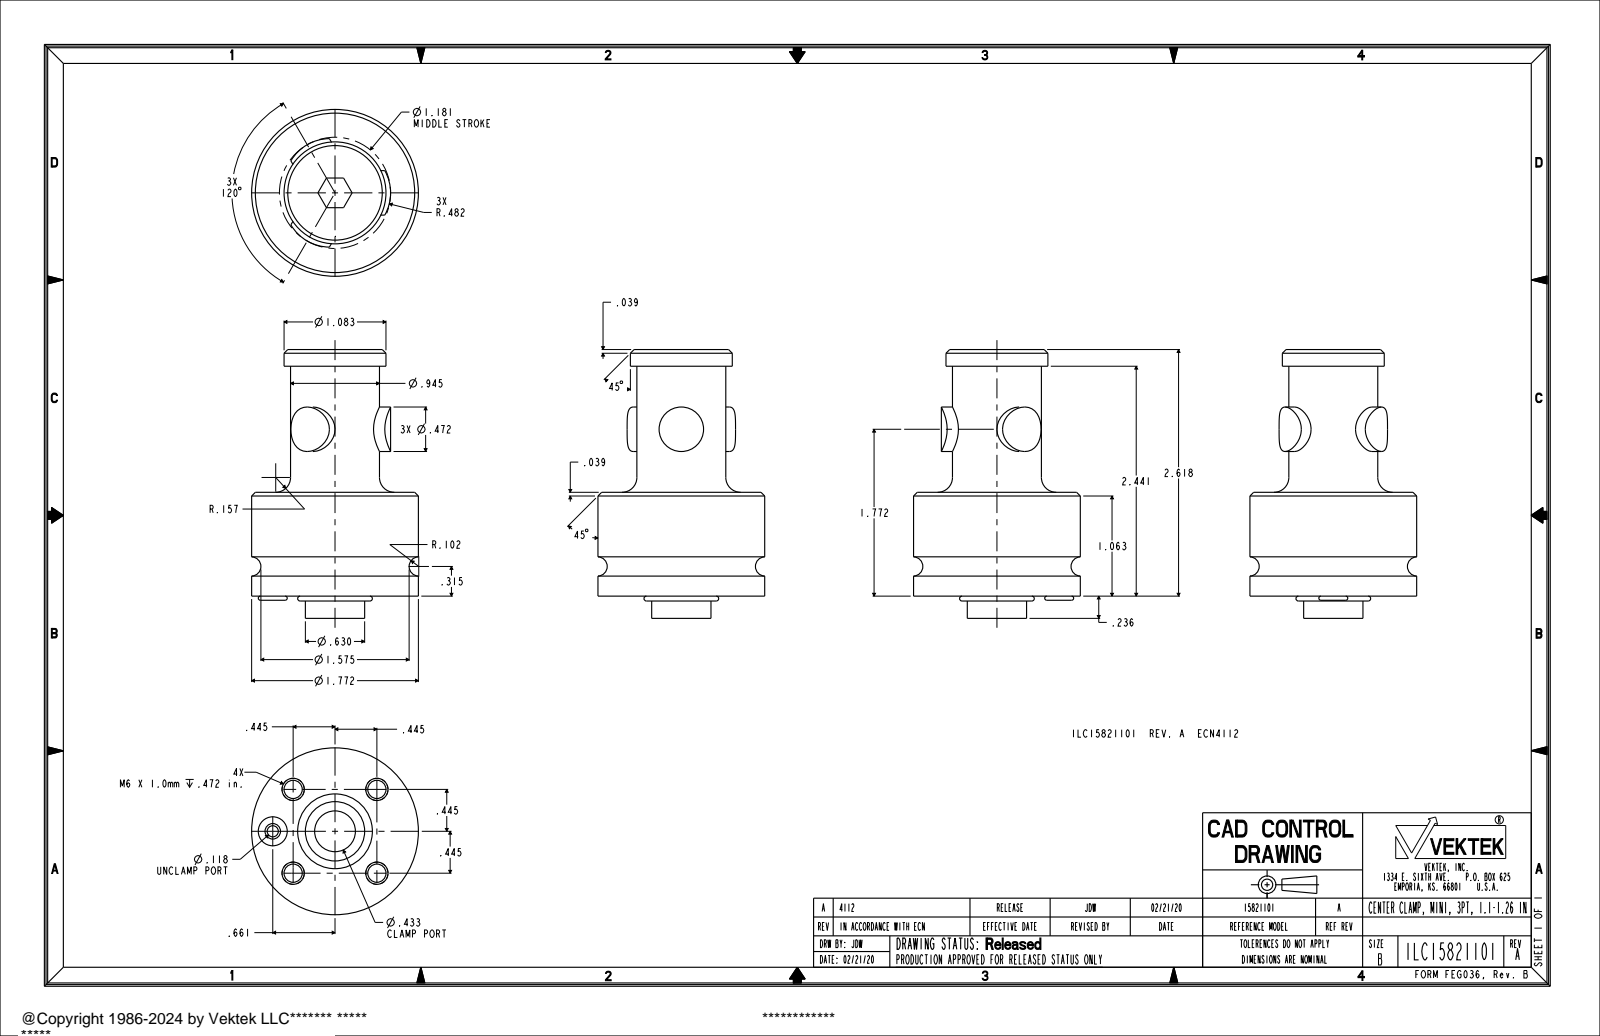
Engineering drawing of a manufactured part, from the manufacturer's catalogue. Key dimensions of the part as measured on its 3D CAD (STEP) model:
Part name (STEP PRODUCT): ILC15821101
STEP written by: PRO/ENGINEER BY PARAMETRIC TECHNOLOGY CORPORATION, 2013320 (AUTOMOTIVE_DESIGN)
Units: inches
Bodies: 1 solid, 97 faces (26 planar, 39 cylindrical, 32 other)
Overall size (bounding box): 2.854 × 1.772 × 1.772
Volume: 3.775 in³ · Surface area: 21.14 in²
Round holes (diameter × count): ⌀0.194 ×4, ⌀0.118 ×1, ⌀0.433 ×1
Round bosses / shafts (diameter × count): ⌀0.236 ×4, ⌀0.472 ×3, ⌀1.772 ×1, ⌀1.083 ×1, ⌀0.945 ×1, ⌀0.63 ×1
Partial cylindrical surfaces — rounded edges, fillets, slot ends (radius × count): R0.482 ×3
Main face-to-face distances: 1.102, 2.618, 1.516, 1.339, 0.236, 2.441, 0.177, 2.677, 2.854, 0.197
Hole centre spacings: 0.629, 0.89, 0.495, 1.193, 1.258, 0.661
